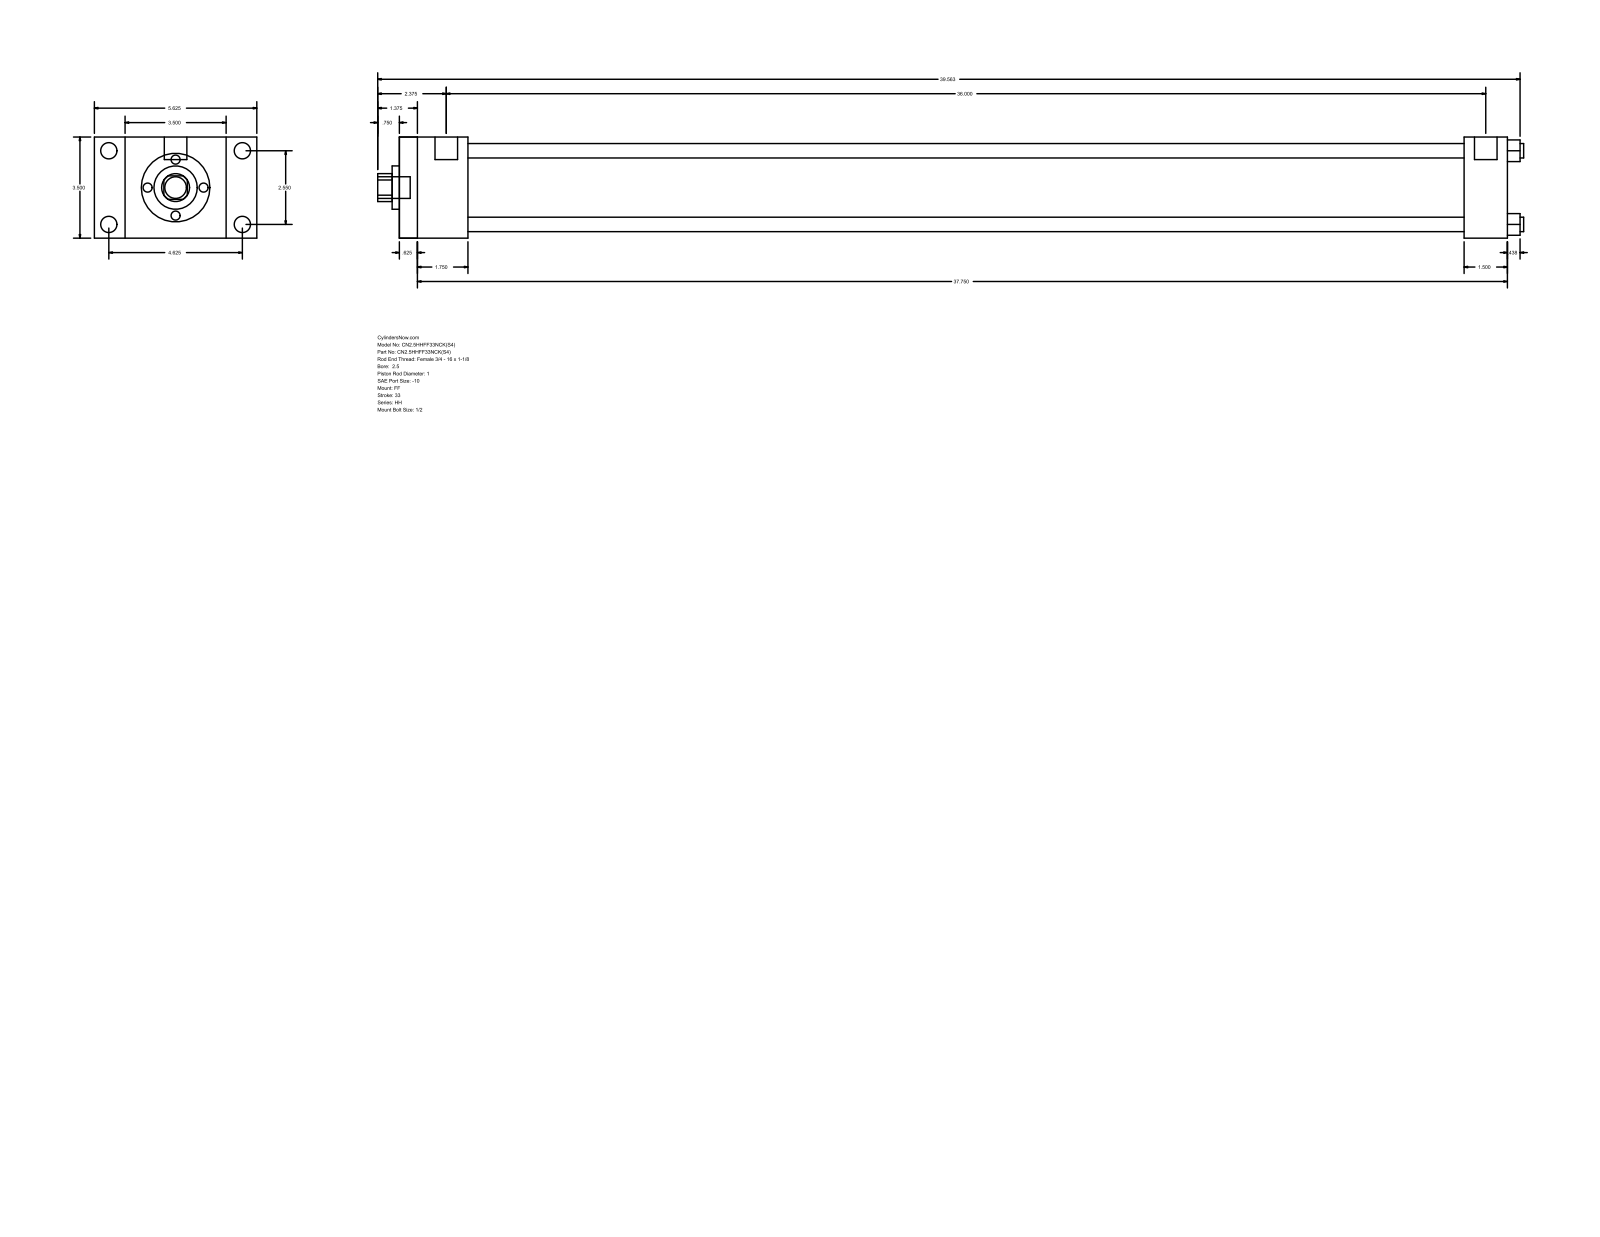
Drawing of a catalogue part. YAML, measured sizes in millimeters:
part_name: "HH_FF__0250_1"
step_written_by: "GSSL Pune (CONFIG_CONTROL_DESIGN)"
units: millimeters
bodies: {solids: 0, faces: 92, planar: 64, cylindrical: 28, other: 0}
overall_size: [1008.06, 142.88, 88.9]
round_holes:
  - {diameter: 12.7, count: 4}
  - {diameter: 25.4, count: 1}
  - {diameter: 38.1, count: 1}
  - {diameter: 73.03, count: 1}
round_bosses_or_shafts:
  - {diameter: 14.3, count: 4}
  - {diameter: 5.56, count: 4}
  - {diameter: 19.84, count: 2}
  - {diameter: 19.05, count: 1}
partial_cylinders:
  - {radius: 12.29, count: 1}
face_to_face_distances: [88.9, 974.72, 15.87, 958.85, 60.33, 44.46, 914.39, 936.62, 920.75, 876.29]
hole_center_spacings: [45.79, 64.76, 91.58]
